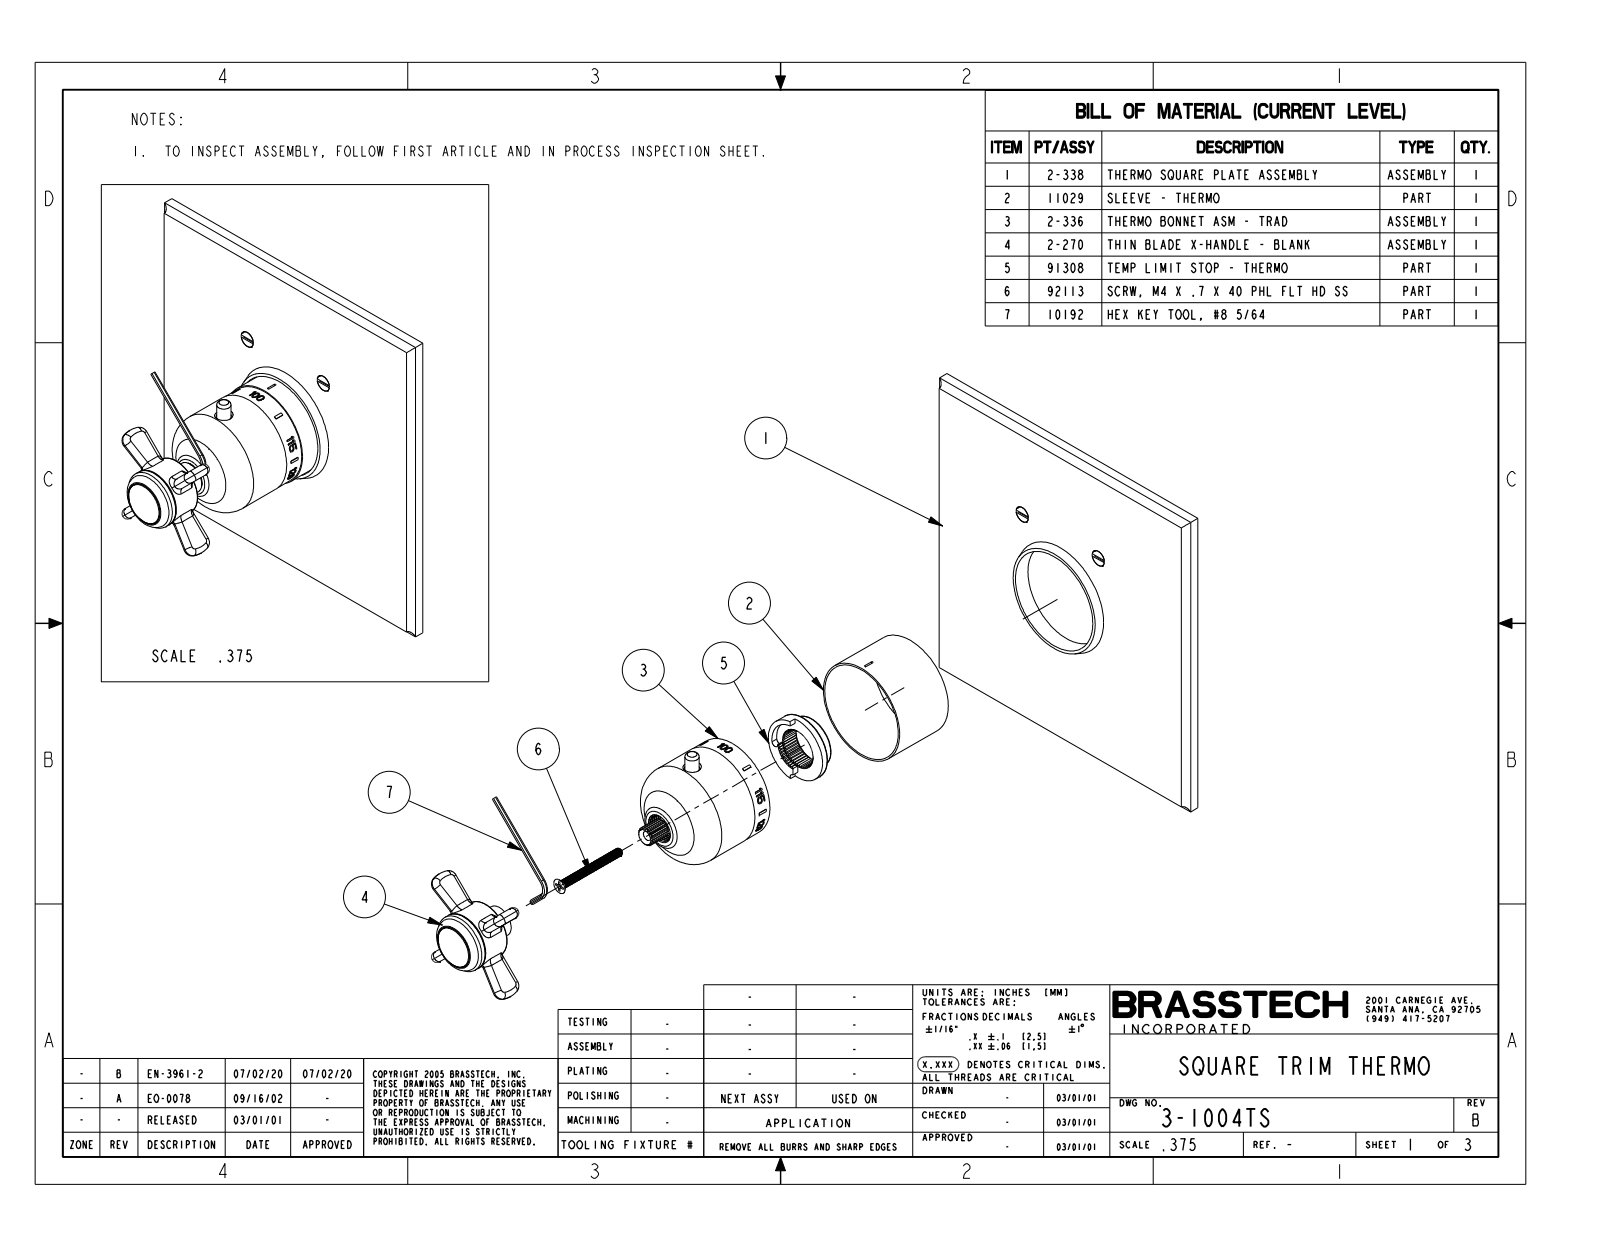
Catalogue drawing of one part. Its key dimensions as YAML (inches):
part_name: "3-1004TS"
step_written_by: "CREO PARAMETRIC BY PTC INC, 2018400 (CONFIG_CONTROL_DESIGN)"
units: inches
bodies: {solids: 1, faces: 489, planar: 342, cylindrical: 61, other: 86}
overall_size: [6.5, 6.5, 4.119]
volume: 20.63
surface_area: 113.5
round_holes:
  - {diameter: 0.815, count: 1}
round_bosses_or_shafts:
  - {diameter: 1.97, count: 1}
  - {diameter: 1.94, count: 1}
  - {diameter: 1.929, count: 1}
  - {diameter: 1.115, count: 1}
  - {diameter: 1.1, count: 1}
  - {diameter: 0.8, count: 1}
  - {diameter: 0.603, count: 1}
  - {diameter: 0.37, count: 1}
partial_cylinders:
  - {radius: 0.1, count: 14}
  - {radius: 0.125, count: 4}
  - {radius: 0.969, count: 1}
face_to_face_distances: [0.313, 6.5, 0.2, 3.129, 2.816, 3.849, 3.536, 0.72, 2.748, 2.435]
